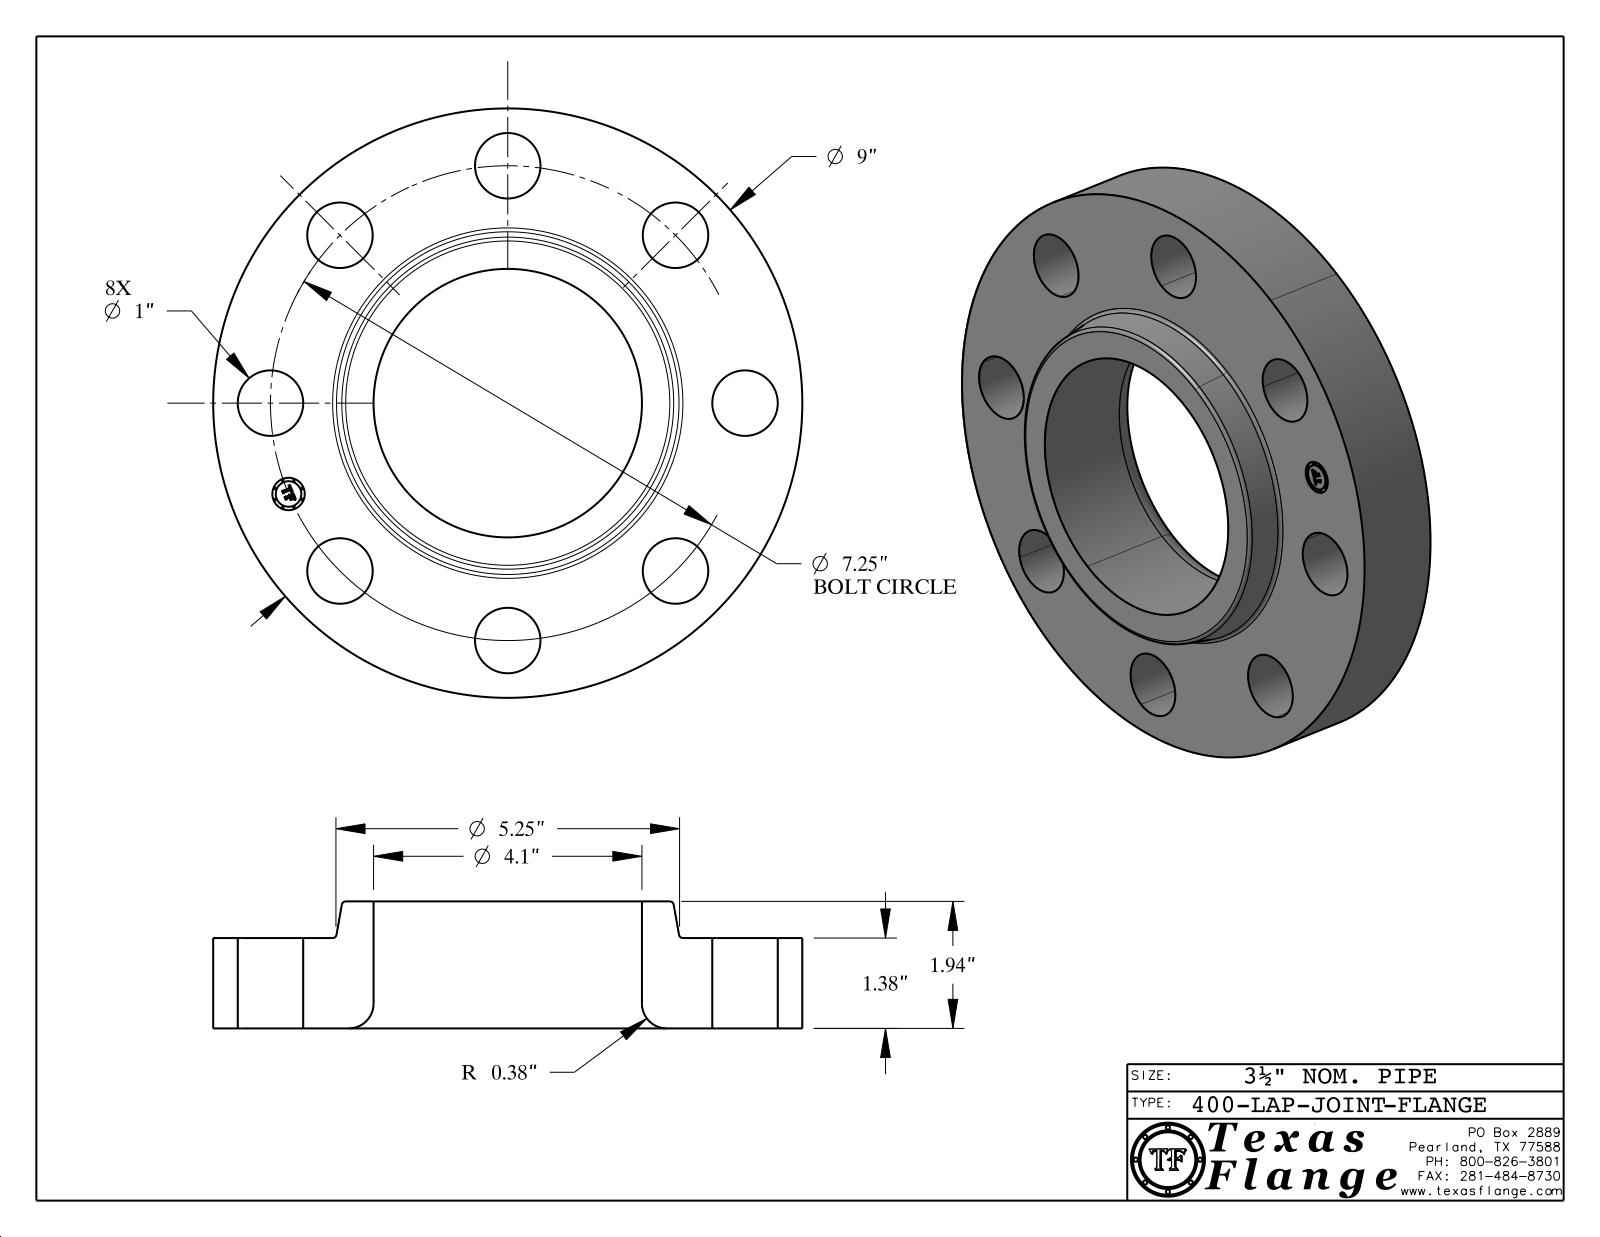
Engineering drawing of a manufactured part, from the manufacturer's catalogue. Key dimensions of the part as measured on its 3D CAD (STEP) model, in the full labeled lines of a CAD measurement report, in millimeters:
Part name (STEP PRODUCT): 400-LAP-JOINT FLANGE
STEP written by: CATIA V5 STEP AP214 (AUTOMOTIVE_DESIGN)
Units: millimetres
Bodies: 1 solid, 416 faces (368 planar, 40 cylindrical, 8 other)
Overall size (bounding box): 228.6 × 228.6 × 49.3
Volume: 1 061 000 mm³ · Surface area: 123 900 mm²
Round holes (diameter × count): ⌀25.4 ×8, ⌀12.6 ×1, ⌀104.1 ×1
Round bosses / shafts (diameter × count): ⌀0.8 ×8, ⌀228.6 ×1, ⌀9.9 ×1
Main face-to-face distances: 35.1, 49.3, 14.2, 34.7, 0.4, 14.6, 3.8, 3.7, 0.7, 2.4
Hole centre spacings: 92.1, 70.5, 130.2, 170.1, 184.2, 35.9, 180.6, 102.3
